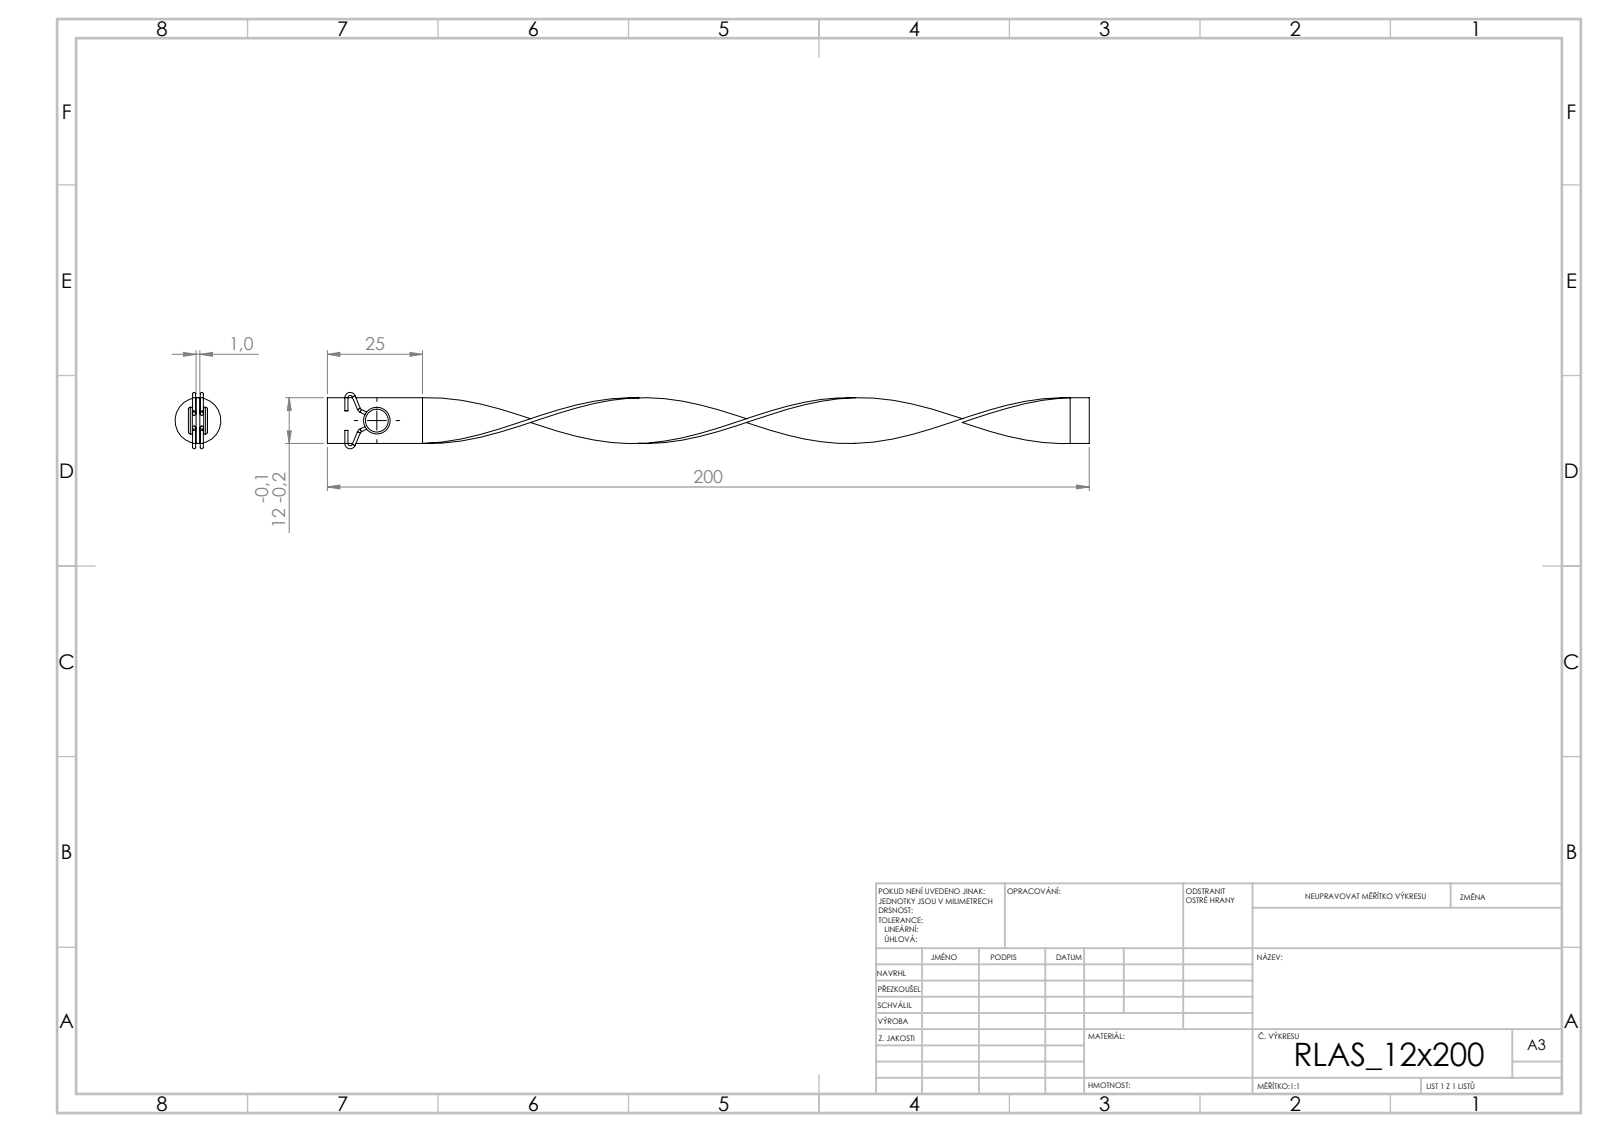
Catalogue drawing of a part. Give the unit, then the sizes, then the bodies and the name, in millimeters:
Units: millimetres
Overall size (bounding box): 200 × 14.8 × 12.04
Round bosses / shafts (diameter × count): ⌀0.8 ×14, ⌀7 ×1, ⌀4 ×1
Main face-to-face distances: 1, 2, 3, 4, 12, 5, 200, 3.45, 8.55, 5.1
Volume: 2 538 mm³ · Surface area: 5 656 mm²
Bodies: 3 solids, 90 faces (18 planar, 40 cylindrical, 32 other)
STEP written by: SolidWorks 2019 (CONFIG_CONTROL_DESIGN)
